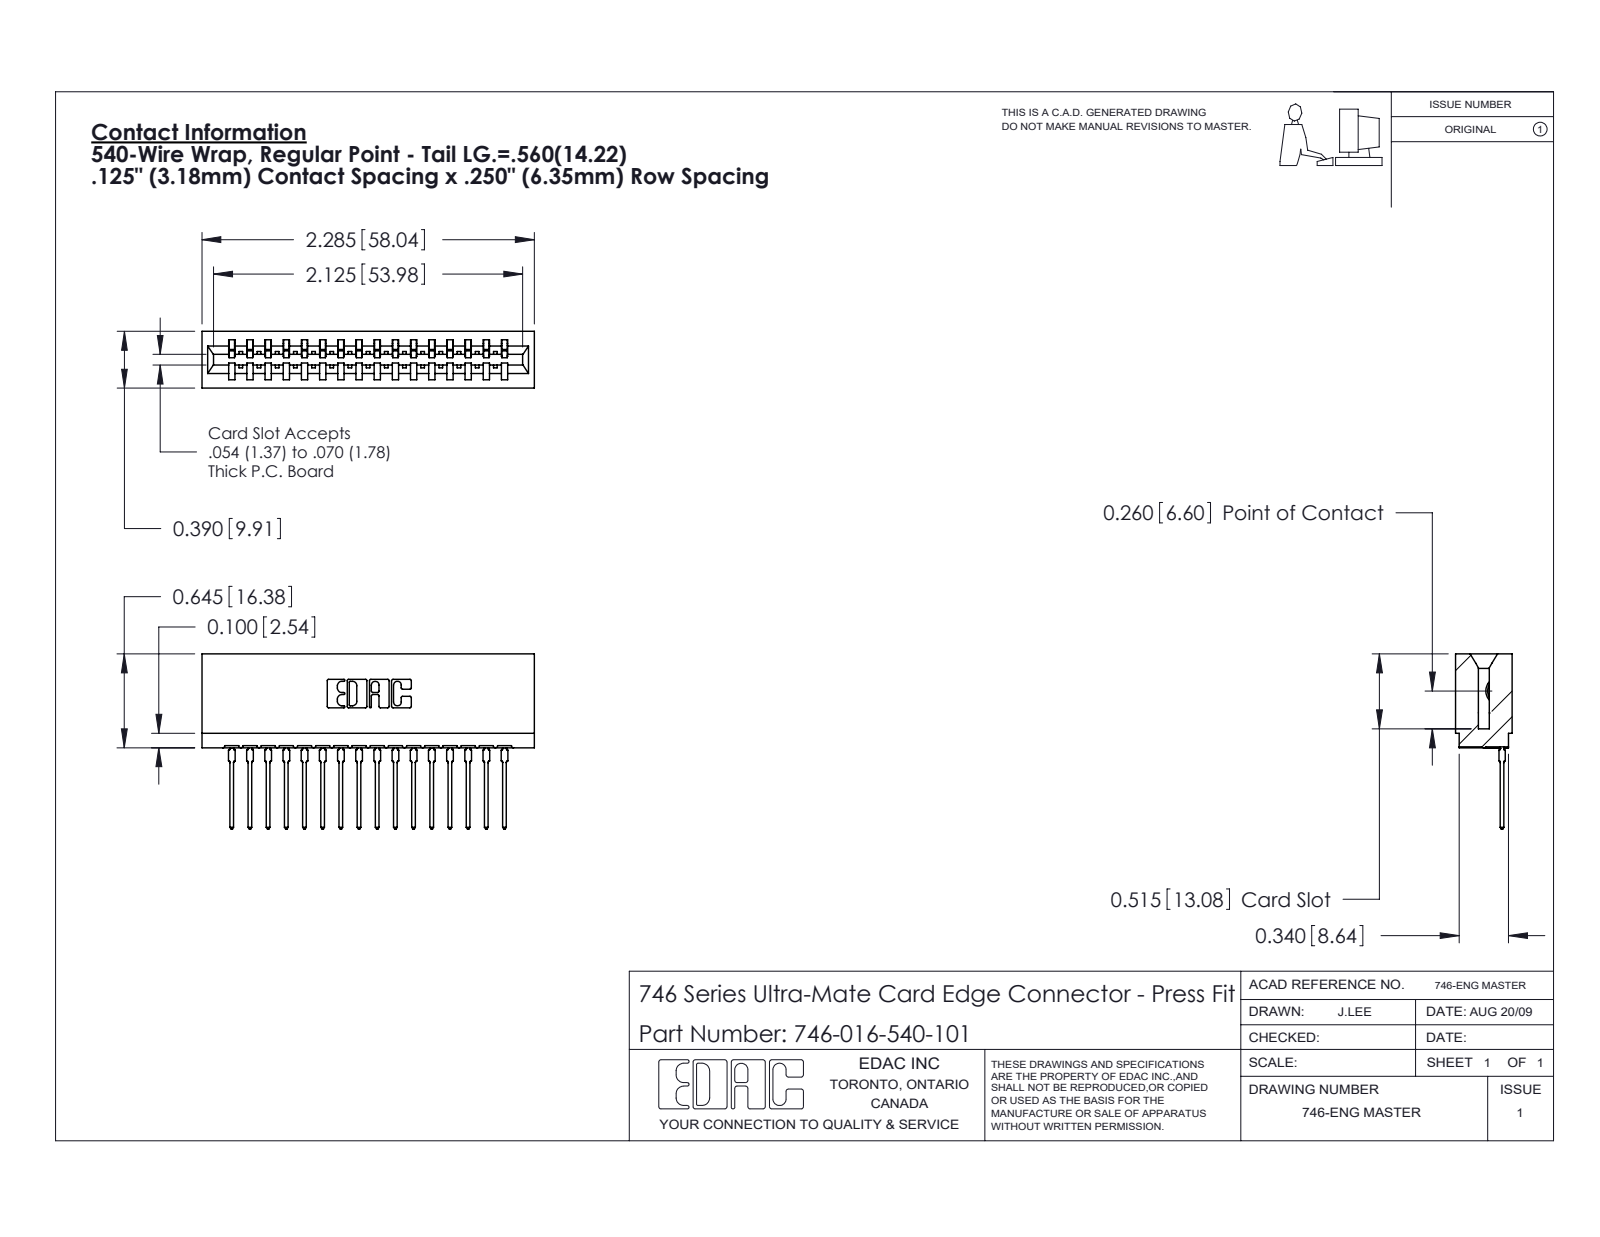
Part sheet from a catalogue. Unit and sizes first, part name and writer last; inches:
Units: inches
Overall size (bounding box): 2.285 × 1.204 × 0.39
Partial cylindrical surfaces — rounded edges, fillets, slot ends (radius × count): R0.021 ×32, R0.01 ×22, R0.015 ×17, R0.007 ×6, R0.031 ×6, R0.005 ×4, R0.011 ×4, R0.026 ×3
Main face-to-face distances: 0.25, 0.333, 0.057, 0.5, 0.39, 0.125, 0.025, 0.042, 0.208, 0.125
Volume: 0.383 in³ · Surface area: 14.05 in²
Bodies: 17 solids, 1825 faces (1063 planar, 346 cylindrical, 416 other)
Part name (STEP PRODUCT): 746-292-001_540; 746 Part_.515 Slot Depth - 01; 746-016-540-101
STEP written by: SolidWorks 2020 (CONFIG_CONTROL_DESIGN)
